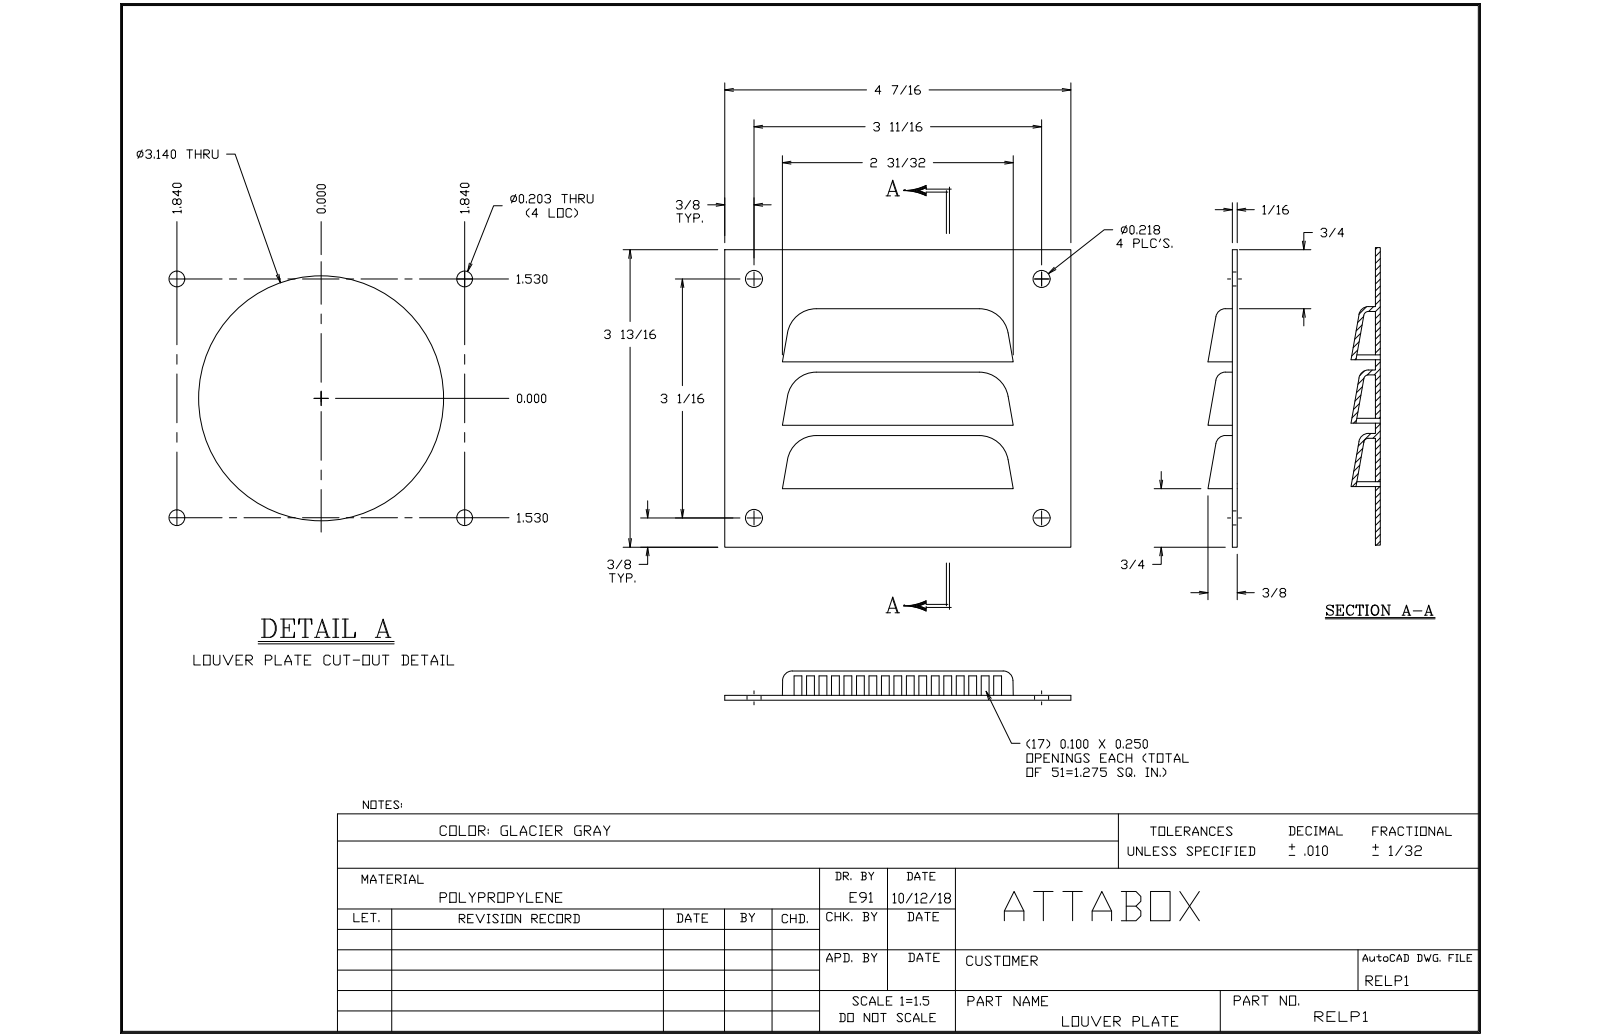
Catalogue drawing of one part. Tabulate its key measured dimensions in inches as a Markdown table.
| quantity | value |
| --- | --- |
| part name | RELP1 |
| STEP written by | SolidWorks 2018 (AUTOMOTIVE_DESIGN) |
| units | inches |
| bodies | 1 solid, 290 faces (242 planar, 34 cylindrical, 14 other) |
| overall size | 4.438 × 3.813 × 0.405 |
| volume | 1.311 in³ |
| surface area | 45.11 in² |
| round holes (diameter × count) | 0.218 × 4 |
| partial cylindrical surfaces (radius × count) | 0.1 × 9, 0.038 × 6, 0.187 × 6, 0.25 × 6, 0.037 × 3 |
| main face-to-face distances | 0.063, 0.144, 0.85, 0.289, 0.082, 0.207, 0.591, 0.03, 0.093, 1.7 |
| hole center spacings | 3.062, 3.687, 4.793 |
